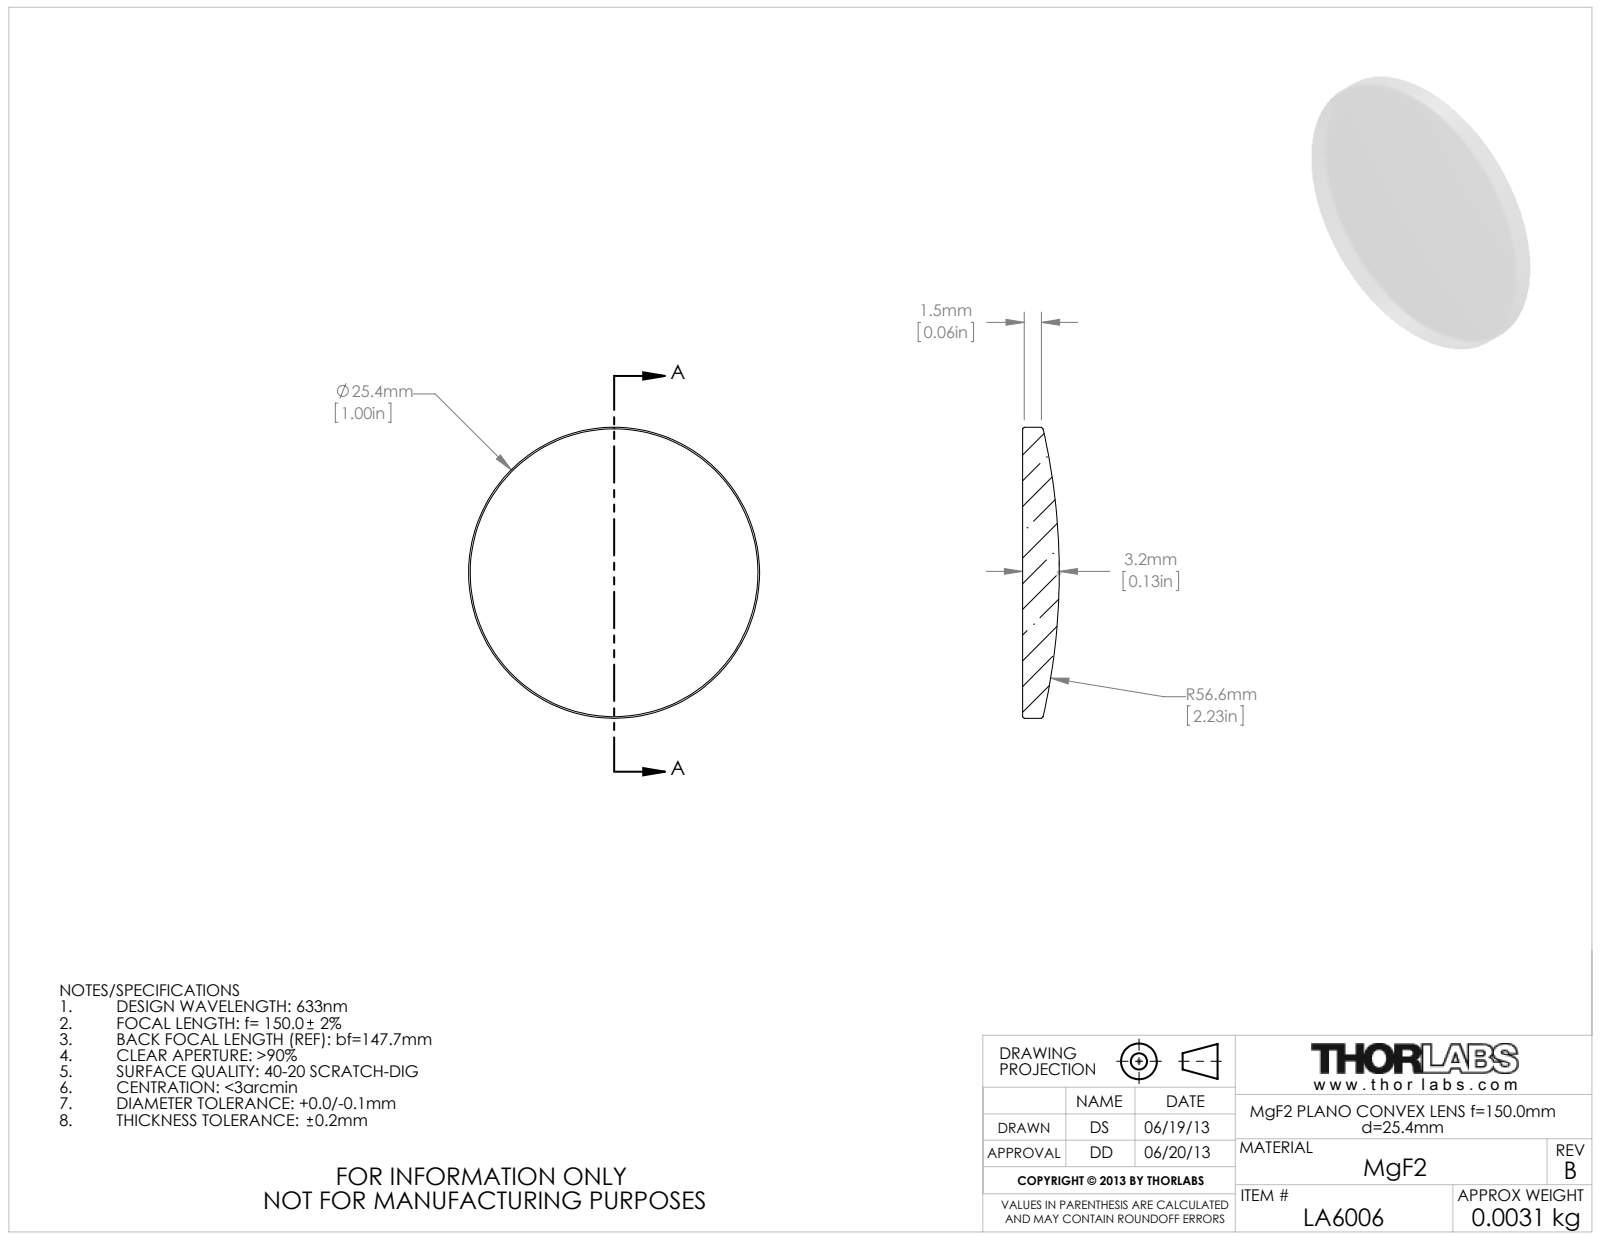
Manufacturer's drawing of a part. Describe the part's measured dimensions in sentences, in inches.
The part is named "7257-E0W". Its 3-D file was written by "SolidWorks 2007 (AUTOMOTIVE_DESIGN)". It is 0 solids with 5 faces: 1 planar, 2 cylindrical and 2 other. Overall it measures 1 by 1 by 0.126 inches. Round bosses or shafts: 1 of diameter 1.
